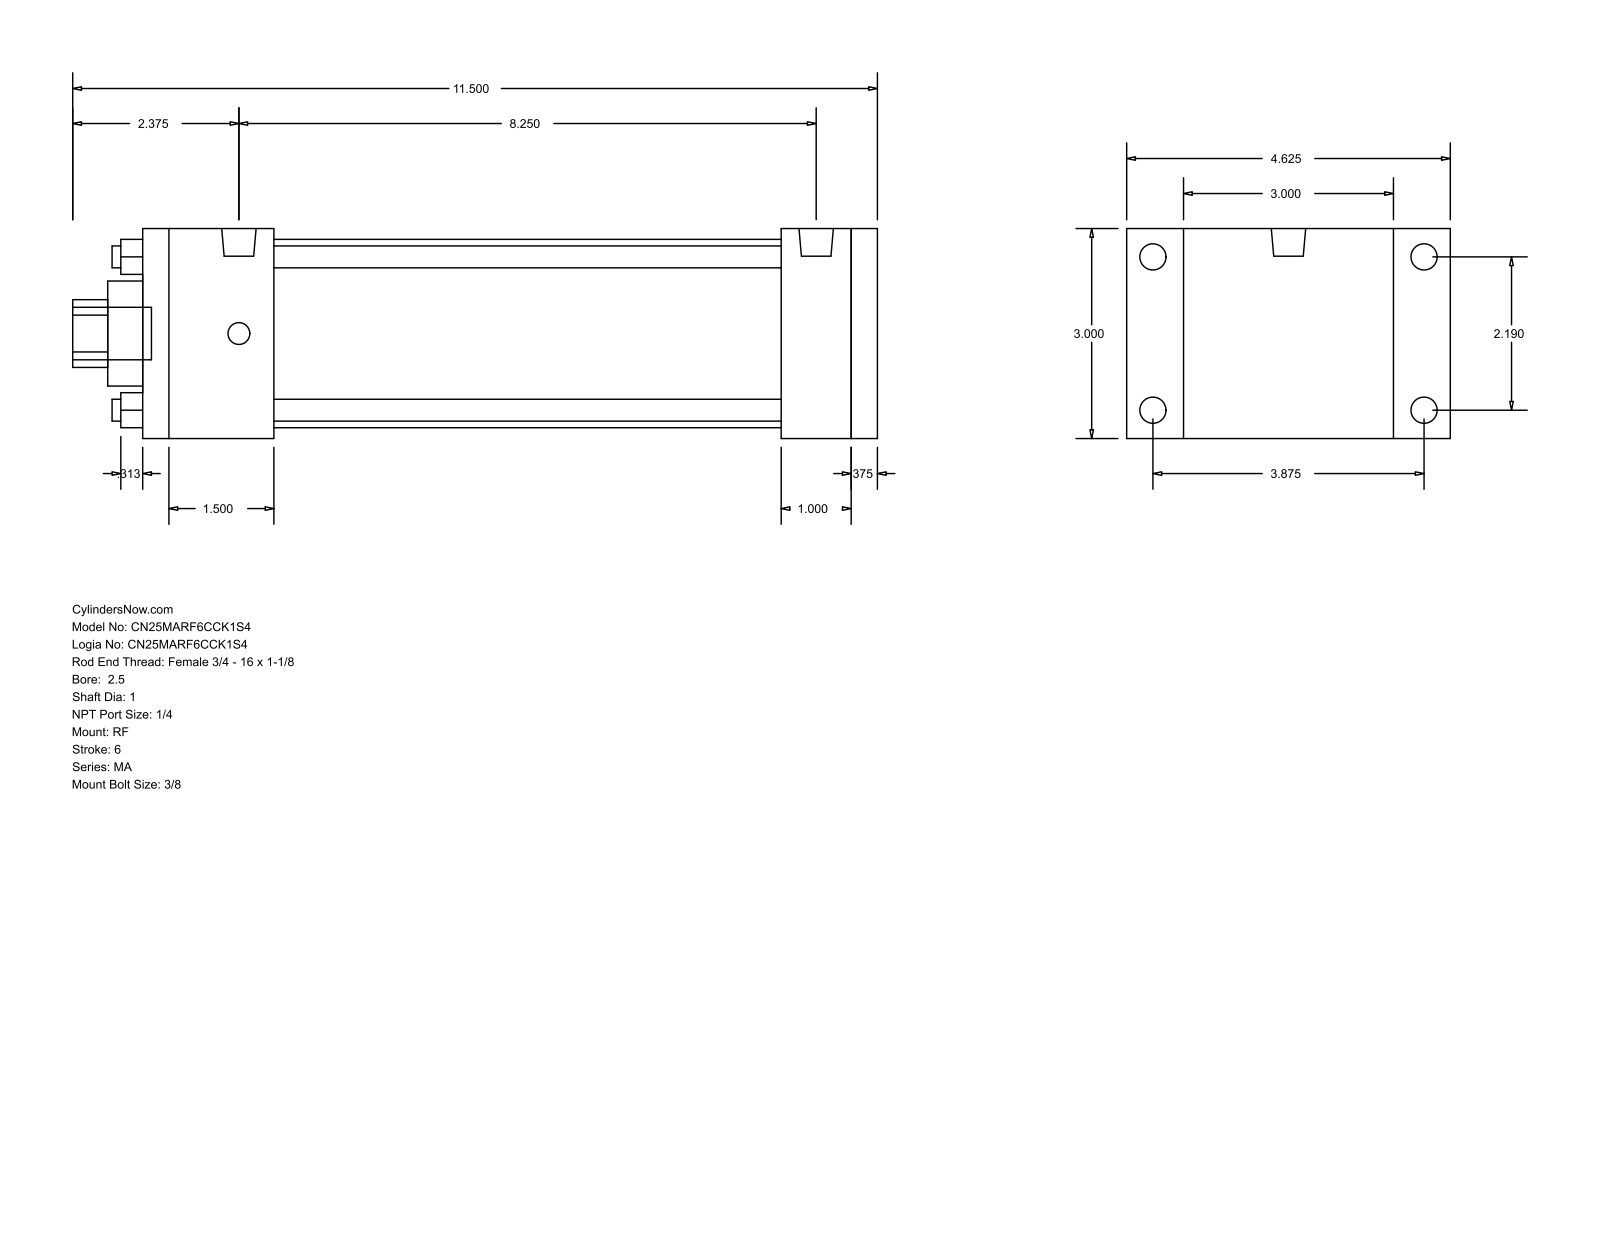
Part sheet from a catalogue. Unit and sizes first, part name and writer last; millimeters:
Units: millimetres
Overall size (bounding box): 292.1 × 117.47 × 76.2
Round holes (diameter × count): ⌀7.94 ×4, ⌀25.4 ×1, ⌀38.1 ×1, ⌀68.33 ×1
Round bosses / shafts (diameter × count): ⌀9.53 ×4, ⌀7.94 ×4, ⌀12.49 ×2, ⌀19.05 ×1
Partial cylindrical surfaces — rounded edges, fillets, slot ends (radius × count): R12.29 ×1
Main face-to-face distances: 76.2, 266.7, 9.53, 257.17, 47.63, 231.78, 184.15, 209.54, 219.07, 25.39
Hole centre spacings: 39.33, 55.62, 78.66
Bodies: 0 solids, 92 faces (64 planar, 28 cylindrical, 0 other)
Part name (STEP PRODUCT): MA_RF__0250_1
STEP written by: GSSL Pune (CONFIG_CONTROL_DESIGN)
